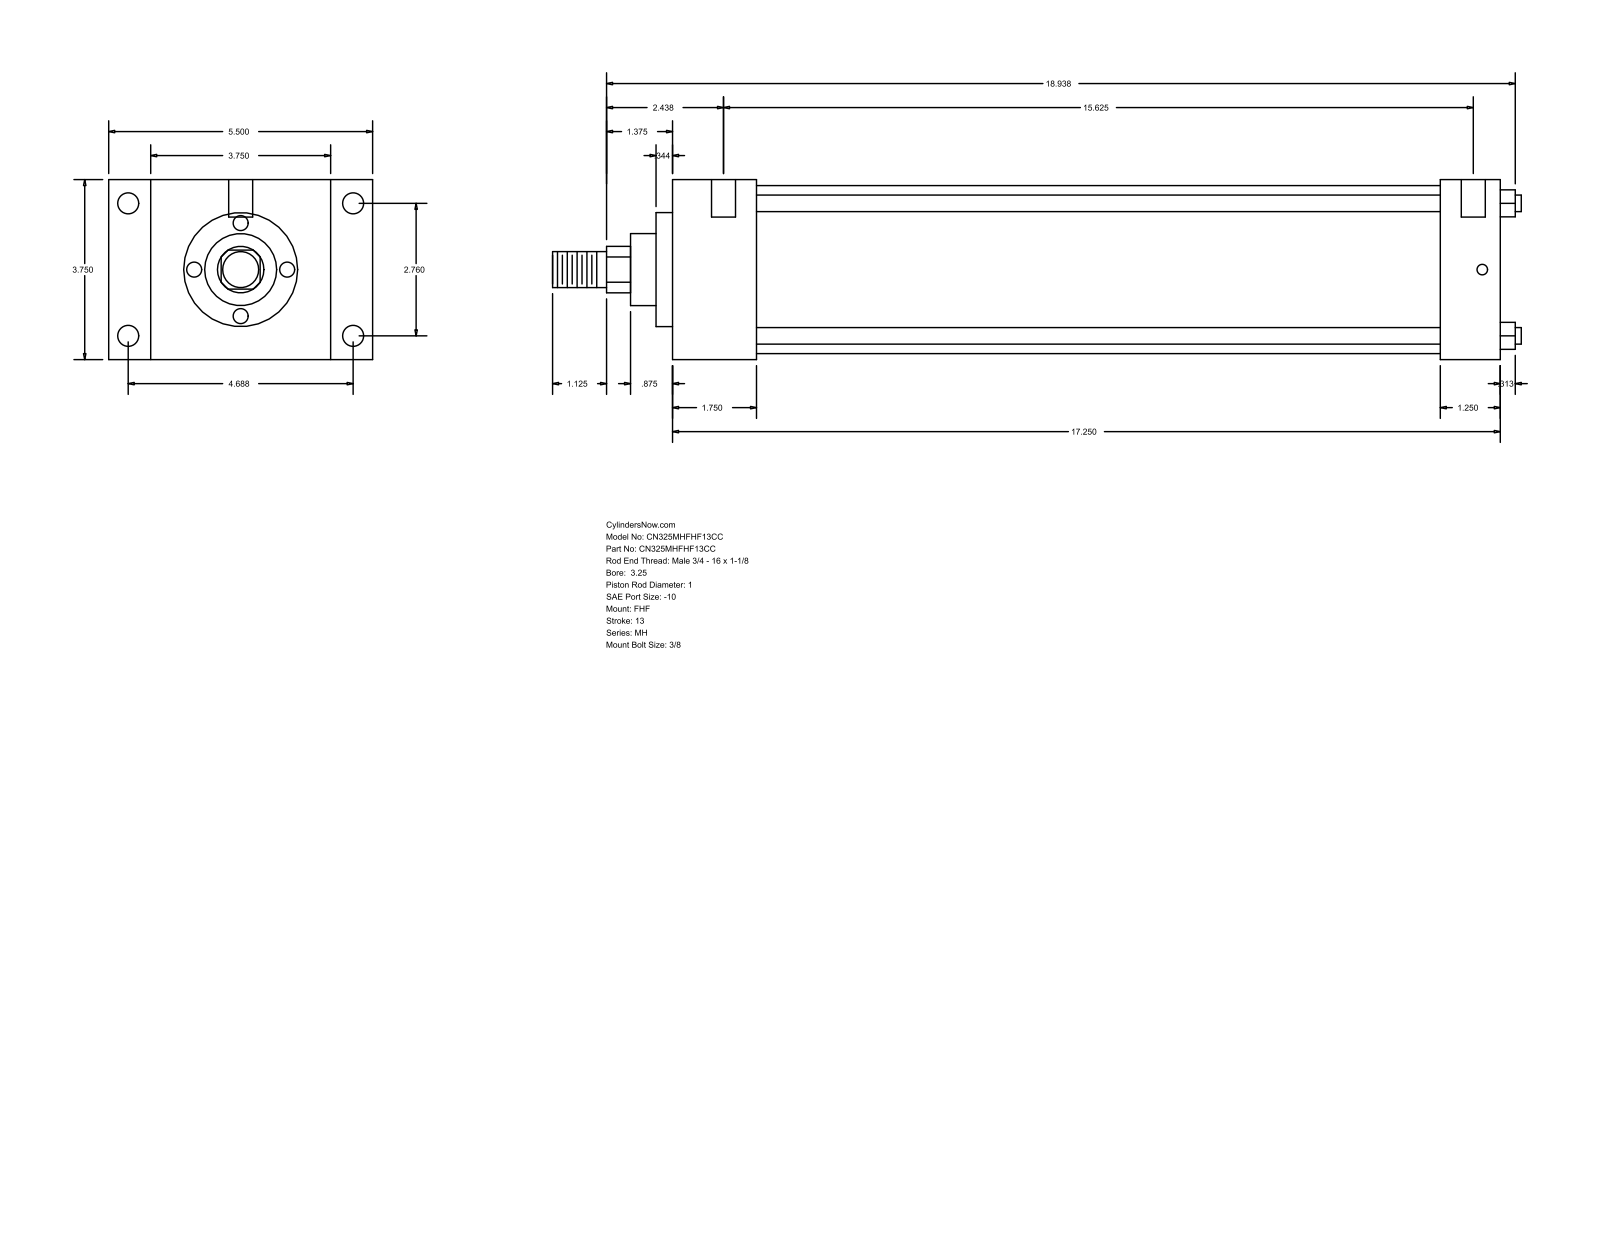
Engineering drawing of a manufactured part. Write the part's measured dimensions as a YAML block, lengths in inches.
part_name: "MH_FHF__0325_1"
step_written_by: "GSSL Pune (CONFIG_CONTROL_DESIGN)"
units: inches
bodies: {solids: 0, faces: 90, planar: 61, cylindrical: 29, other: 0}
overall_size: [20.187, 5.5, 3.75]
round_holes:
  - {diameter: 0.219, count: 4}
  - {diameter: 0.438, count: 4}
  - {diameter: 0.5, count: 2}
round_bosses_or_shafts:
  - {diameter: 0.345, count: 4}
  - {diameter: 3.5, count: 1}
  - {diameter: 2.375, count: 1}
  - {diameter: 1.5, count: 1}
  - {diameter: 1, count: 1}
  - {diameter: 0.75, count: 1}
partial_cylinders:
  - {radius: 0.484, count: 1}
face_to_face_distances: [3.75, 17.25, 1.75, 15.5, 0.875, 4.625, 5.5, 16, 14.25, 1.25]
hole_center_spacings: [2.76, 4.687, 5.439, 15.875, 0.062, 0.187, 15.625, 15.687]
